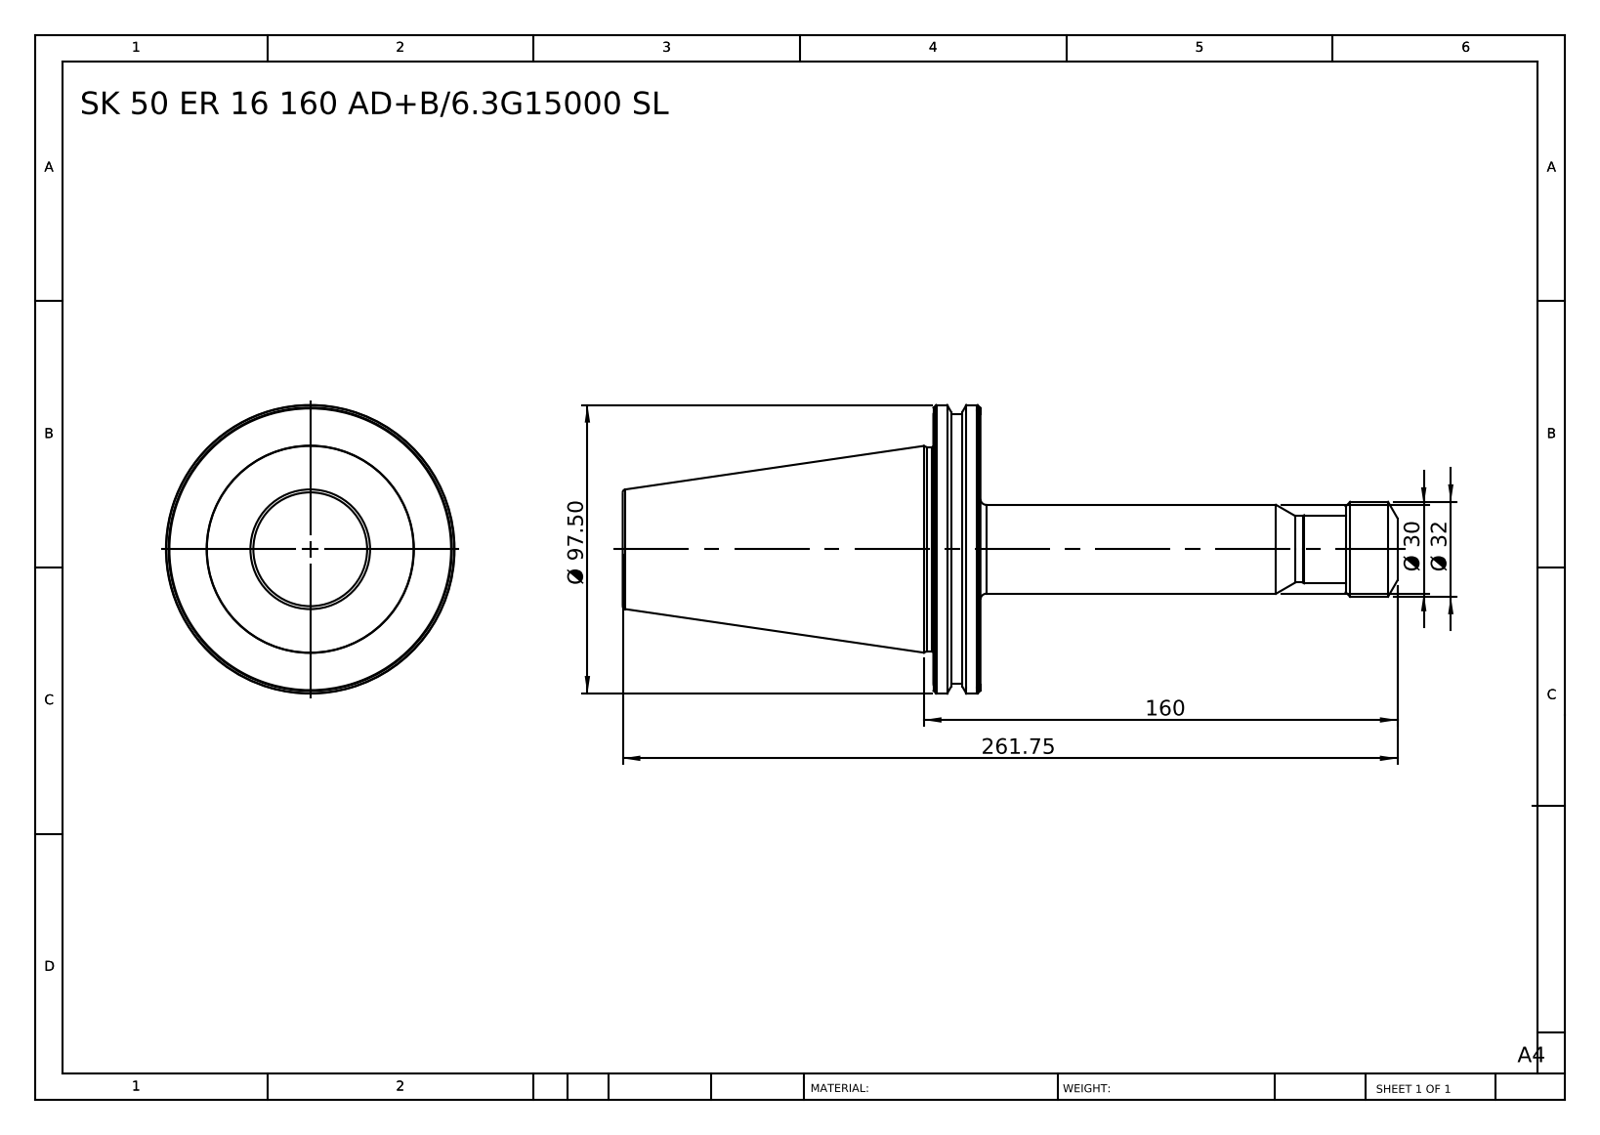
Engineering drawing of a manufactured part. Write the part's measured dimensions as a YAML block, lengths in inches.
part_name: "SK 50 ER 16 160 AD-6.3G15000 SL"
step_written_by: "SolidWorks 2014 (CONFIG_CONTROL_DESIGN)"
units: inches
bodies: {solids: 1, faces: 77, planar: 7, cylindrical: 16, other: 54}
overall_size: [10.305, 3.839, 3.839]
volume: 28.56
surface_area: 77
round_bosses_or_shafts:
  - {diameter: 3.839, count: 1}
  - {diameter: 3.583, count: 1}
  - {diameter: 2.717, count: 1}
  - {diameter: 1.26, count: 1}
  - {diameter: 1.181, count: 1}
  - {diameter: 0.906, count: 1}
  - {diameter: 0.886, count: 1}
face_to_face_distances: [0.626, 4.758, 4.132, 5.547, 6.173, 10.305, 5.787, 5.937, 0.24, 0.39]
